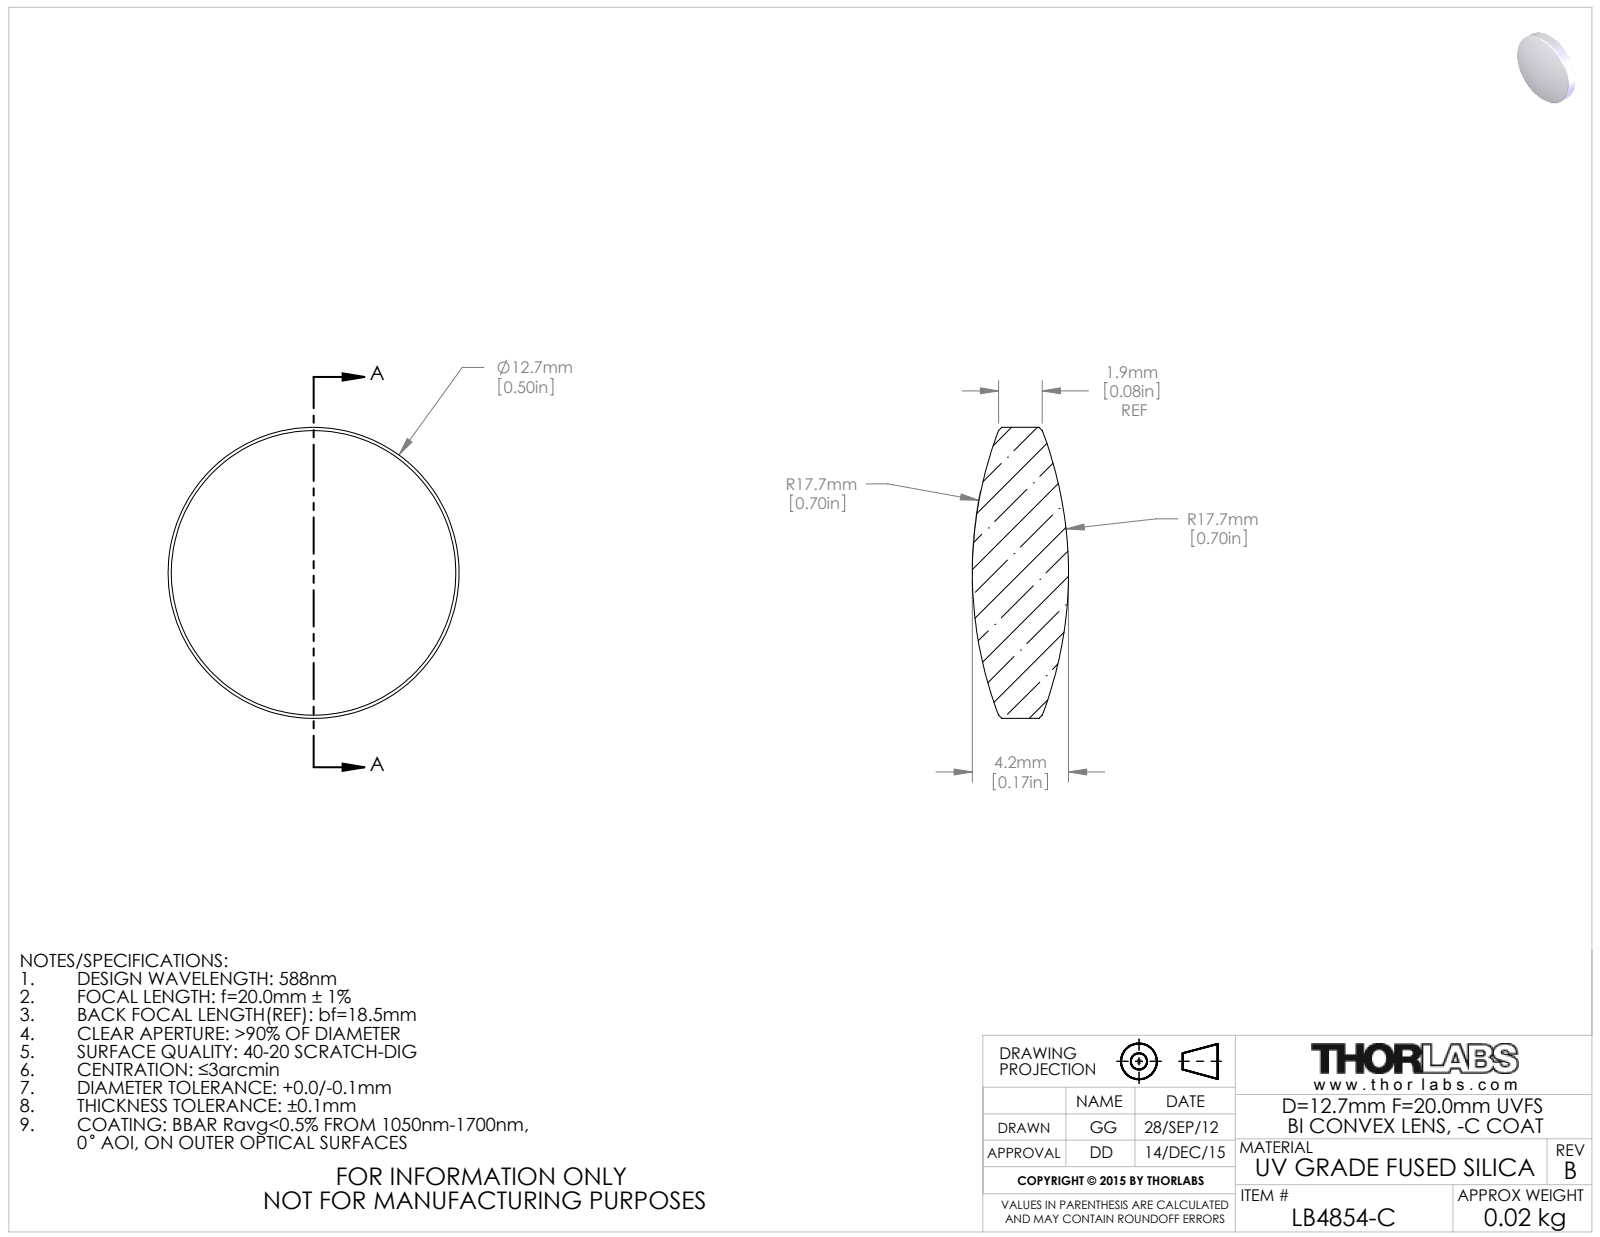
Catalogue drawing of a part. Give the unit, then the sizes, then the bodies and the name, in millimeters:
Units: millimetres
Overall size (bounding box): 12.7 × 12.7 × 4.2
Round bosses / shafts (diameter × count): ⌀12.7 ×1
Volume: 381 mm³ · Surface area: 331 mm²
Bodies: 1 solid, 10 faces (0 planar, 2 cylindrical, 8 other)
Part name (STEP PRODUCT): 25010-E0W
STEP written by: SolidWorks 2011 (CONFIG_CONTROL_DESIGN)
